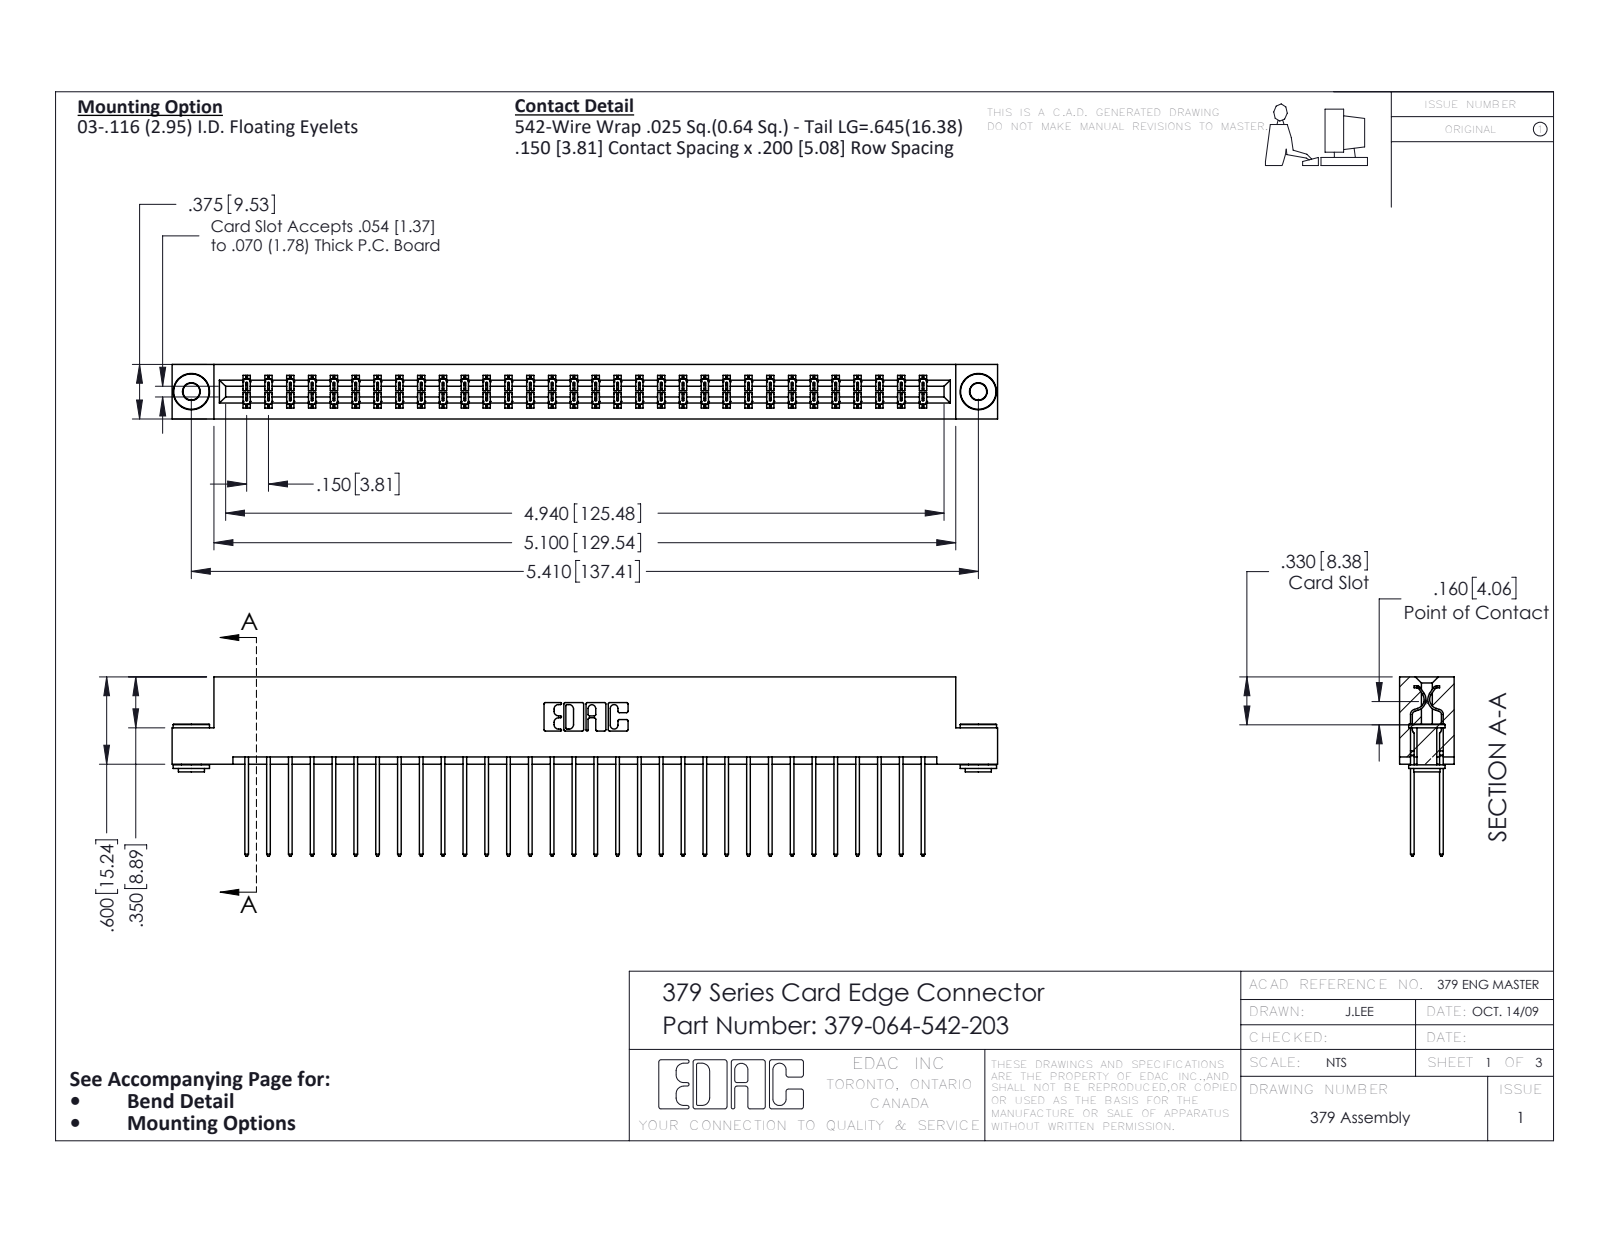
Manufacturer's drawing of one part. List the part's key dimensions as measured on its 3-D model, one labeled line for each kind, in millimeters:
Part name (STEP PRODUCT): 379-064-542-203; 345-250-002_345-250-002-102; 379 Part_Flush - .156 Dia - TH; 345-292-001_345-293-142
STEP written by: SolidWorks 2016 (CONFIG_CONTROL_DESIGN)
Units: millimetres
Bodies: 67 solids, 3480 faces (2384 planar, 1088 cylindrical, 8 other)
Overall size (bounding box): 144.1 × 31.3 × 9.5
Volume: 15 600 mm³ · Surface area: 19 090 mm²
Round holes (diameter × count): ⌀2.9 ×2, ⌀4 ×2
Round bosses / shafts (diameter × count): ⌀6.4 ×2, ⌀4.6 ×2, ⌀3.5 ×2
Partial cylindrical surfaces — rounded edges, fillets, slot ends (radius × count): R0.2 ×96, R0.3 ×64, R0.3 ×22, R0.2 ×6, R0.8 ×6, R0.7 ×3, R0.4 ×2, R0.6 ×2
Main face-to-face distances: 7.6, 1.9, 9.5, 5.1, 2.5, 7, 0.6, 1.9, 3.8, 5.7
Hole centre spacings: 137.4
